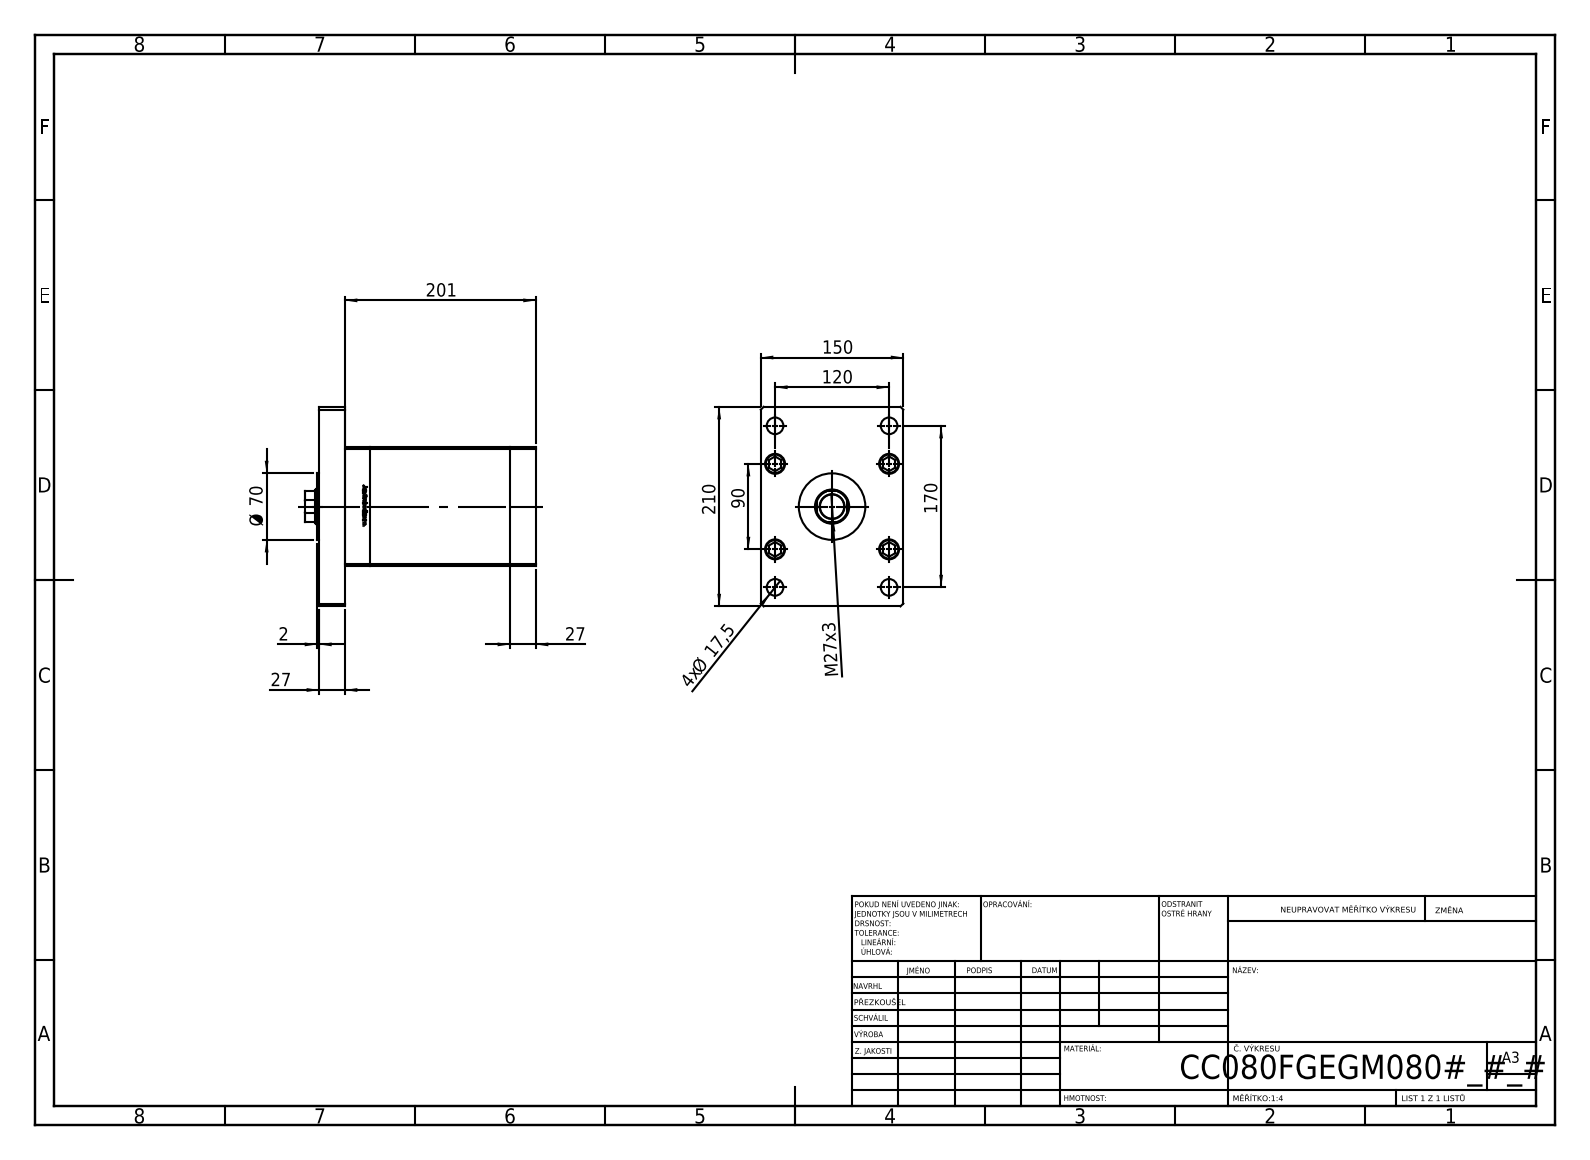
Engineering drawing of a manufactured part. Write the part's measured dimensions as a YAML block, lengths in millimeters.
part_name: "V220C_FRONT_F; ALLEN BOLT; V220C_F; V220C BACK_F (+2 more)"
step_written_by: "SolidWorks 2019 (CONFIG_CONTROL_DESIGN)"
units: millimeters
bodies: {solids: 19, faces: 1310, planar: 517, cylindrical: 187, other: 606}
overall_size: [243, 210, 150]
volume: 4072000
surface_area: 453403
round_holes:
  - {diameter: 17.5, count: 9}
  - {diameter: 22, count: 5}
  - {diameter: 16, count: 4}
  - {diameter: 21, count: 4}
  - {diameter: 2, count: 2}
  - {diameter: 13.16, count: 2}
  - {diameter: 25.5, count: 1}
  - {diameter: 36, count: 1}
  - {diameter: 37.5, count: 1}
round_bosses_or_shafts:
  - {diameter: 8, count: 9}
  - {diameter: 21, count: 5}
  - {diameter: 80, count: 1}
  - {diameter: 70, count: 1}
partial_cylinders:
  - {radius: 0.93, count: 2}
  - {radius: 17.5, count: 1}
face_to_face_distances: [27, 174, 201, 150, 147, 54, 125, 167.5, 228, 33.5]
hole_center_spacings: [51, 40, 75, 104.04, 120, 126.49, 130, 176.92]
